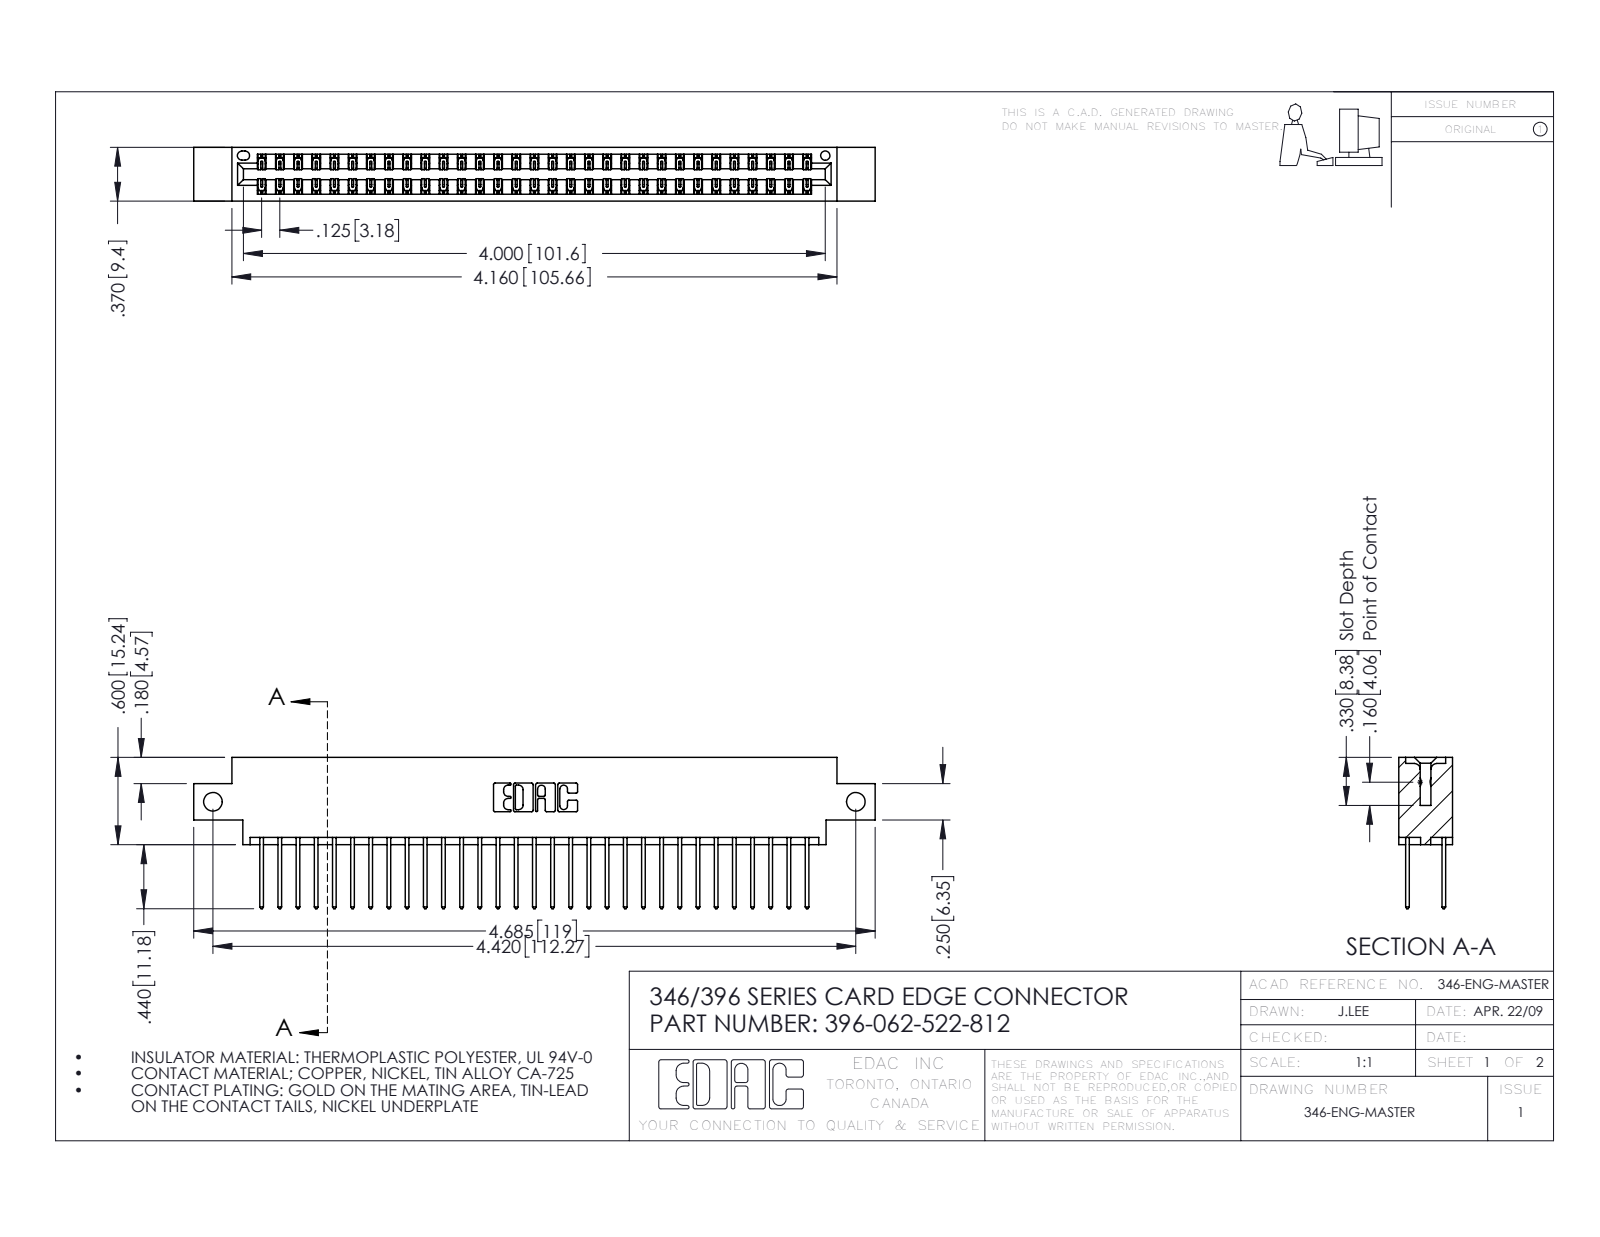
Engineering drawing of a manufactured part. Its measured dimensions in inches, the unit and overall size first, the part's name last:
Units: inches
Overall size (bounding box): 4.685 × 1.04 × 0.37
Round holes (diameter × count): ⌀0.128 ×2, ⌀0.064 ×1
Partial cylindrical surfaces — rounded edges, fillets, slot ends (radius × count): R0.006 ×93, R0.01 ×62, R0.01 ×22, R0.007 ×6, R0.031 ×6, R0.026 ×3, R0.014 ×2, R0.022 ×2
Main face-to-face distances: 0.048, 0.322, 0.25, 0.37, 0.072, 0.298, 0.025, 0.275, 0.148, 0.222
Hole centre spacings: 4.42
Volume: 0.698 in³ · Surface area: 25.3 in²
Bodies: 63 solids, 3350 faces (2250 planar, 1100 cylindrical, 0 other)
Part name (STEP PRODUCT): 345-292-001_345-293-122; 346 Part_0.170 Offset - Side Mount; 396-062-522-812
STEP written by: SolidWorks 2016 (CONFIG_CONTROL_DESIGN)
